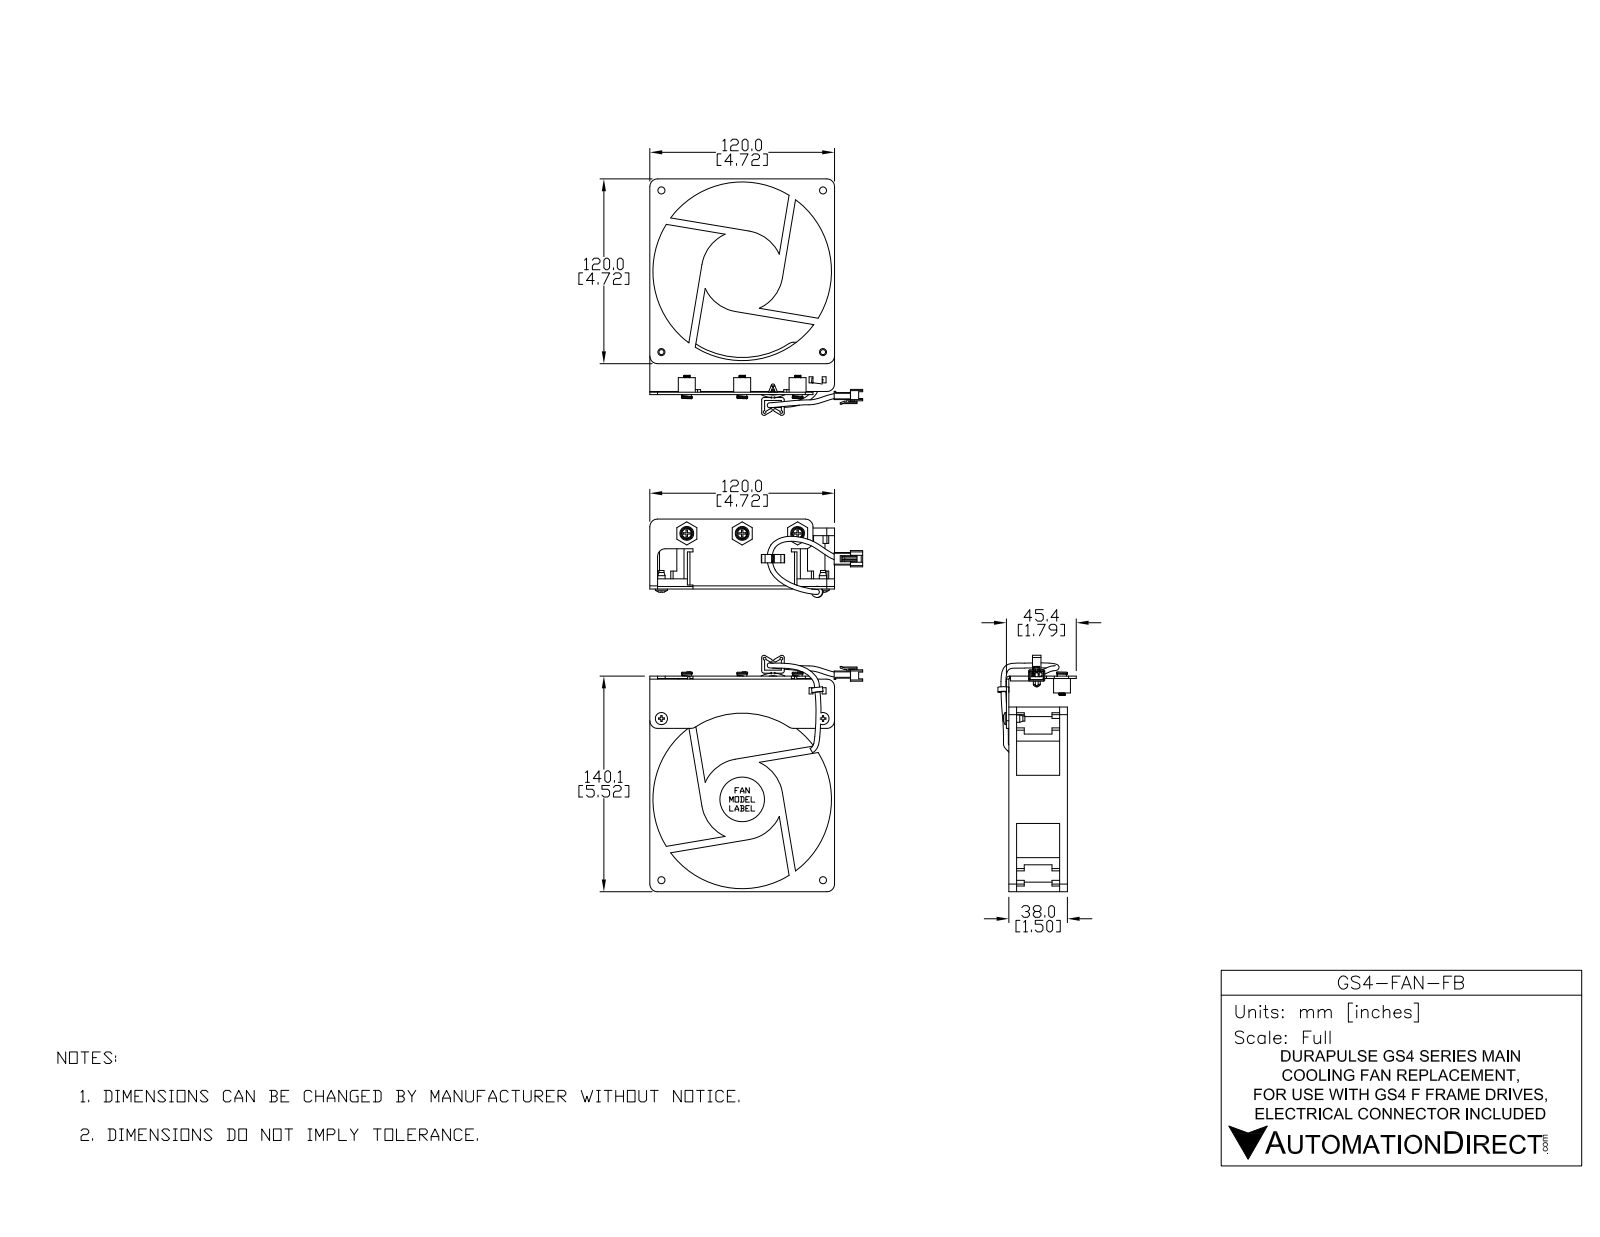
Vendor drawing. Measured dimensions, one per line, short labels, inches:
name: GS4-FAN-FB
written by: SolidWorks 2015 (AUTOMOTIVE_DESIGN)
unit: in
bodies: 0 solids, 445 faces (211 planar, 180 cylindrical, 54 other)
size: 6.047 × 5.445 × 1.872
holes: 4× ⌀0.181, 3× ⌀0.157, 2× ⌀0.071, 1× ⌀4.567
bosses: 3× ⌀0.433, 3× ⌀0.276, 3× ⌀0.236, 2× ⌀0.311, 2× ⌀0.189, 2× ⌀0.13
rounds: 13× R0.197, 6× R0.02, 5× R0.079, 4× R0.004, 4× R0.031, 4× R0.051, 4× R0.059, 3× R0.157
face distances: 0.063, 1.496, 0.197, 4.724, 2.088, 1.299, 1.559, 1.724, 0.182, 1.906
hole spacings: 2.923, 4.134, 1.417, 5.846, 0.429, 1.866, 2.14, 2.835
